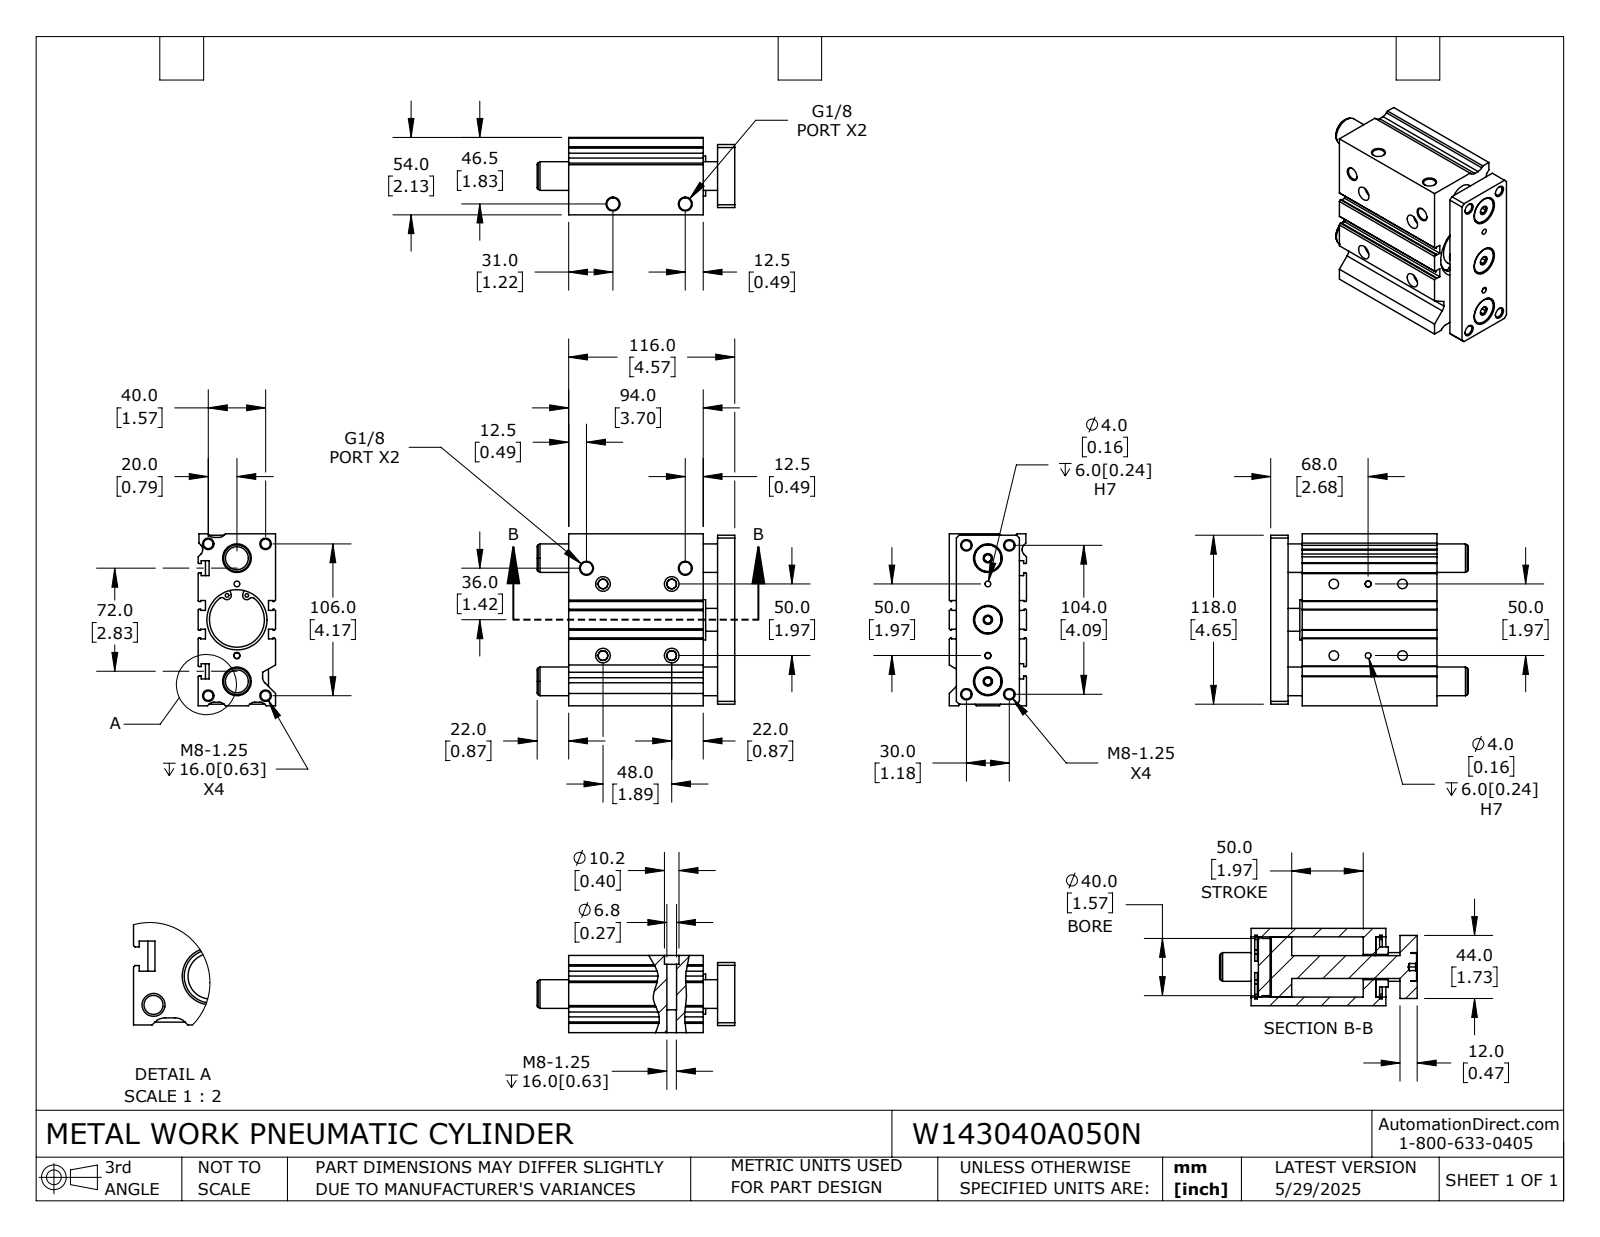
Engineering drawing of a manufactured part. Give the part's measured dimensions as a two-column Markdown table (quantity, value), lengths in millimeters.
| quantity | value |
| --- | --- |
| part name | W143040A050N_BODY; W143040A050N; W143040A050N_ROD |
| STEP written by | SolidWorks 2024 (CONFIG_CONTROL_DESIGN) |
| units | millimeters |
| bodies | 6 solids, 393 faces (192 planar, 151 cylindrical, 50 other) |
| overall size | 138 × 120 × 54 |
| volume | 564 000 mm³ |
| surface area | 134 500 mm² |
| round holes (diameter × count) | 6.7 × 12, 2.5 × 4, 4 × 4, 6.8 × 4, 8.6 × 4, 10.2 × 4, 5 × 3, 20 × 3, 17.7 × 1, 38.4 × 1 |
| round bosses / shafts (diameter × count) | 19 × 3, 44.5 × 2, 42 × 1, 40 × 1, 28 × 1, 16 × 1 |
| partial cylindrical surfaces (radius × count) | 5 × 7, 2 × 4, 2.3 × 4, 2.9 × 4, 4 × 2 |
| main face-to-face distances | 54, 5, 49, 22, 2.5, 116, 12, 10, 104, 94 |
| hole center spacings | 5.1, 10.5, 17.5, 18.3, 22.4, 24, 26.9, 30.9 |
